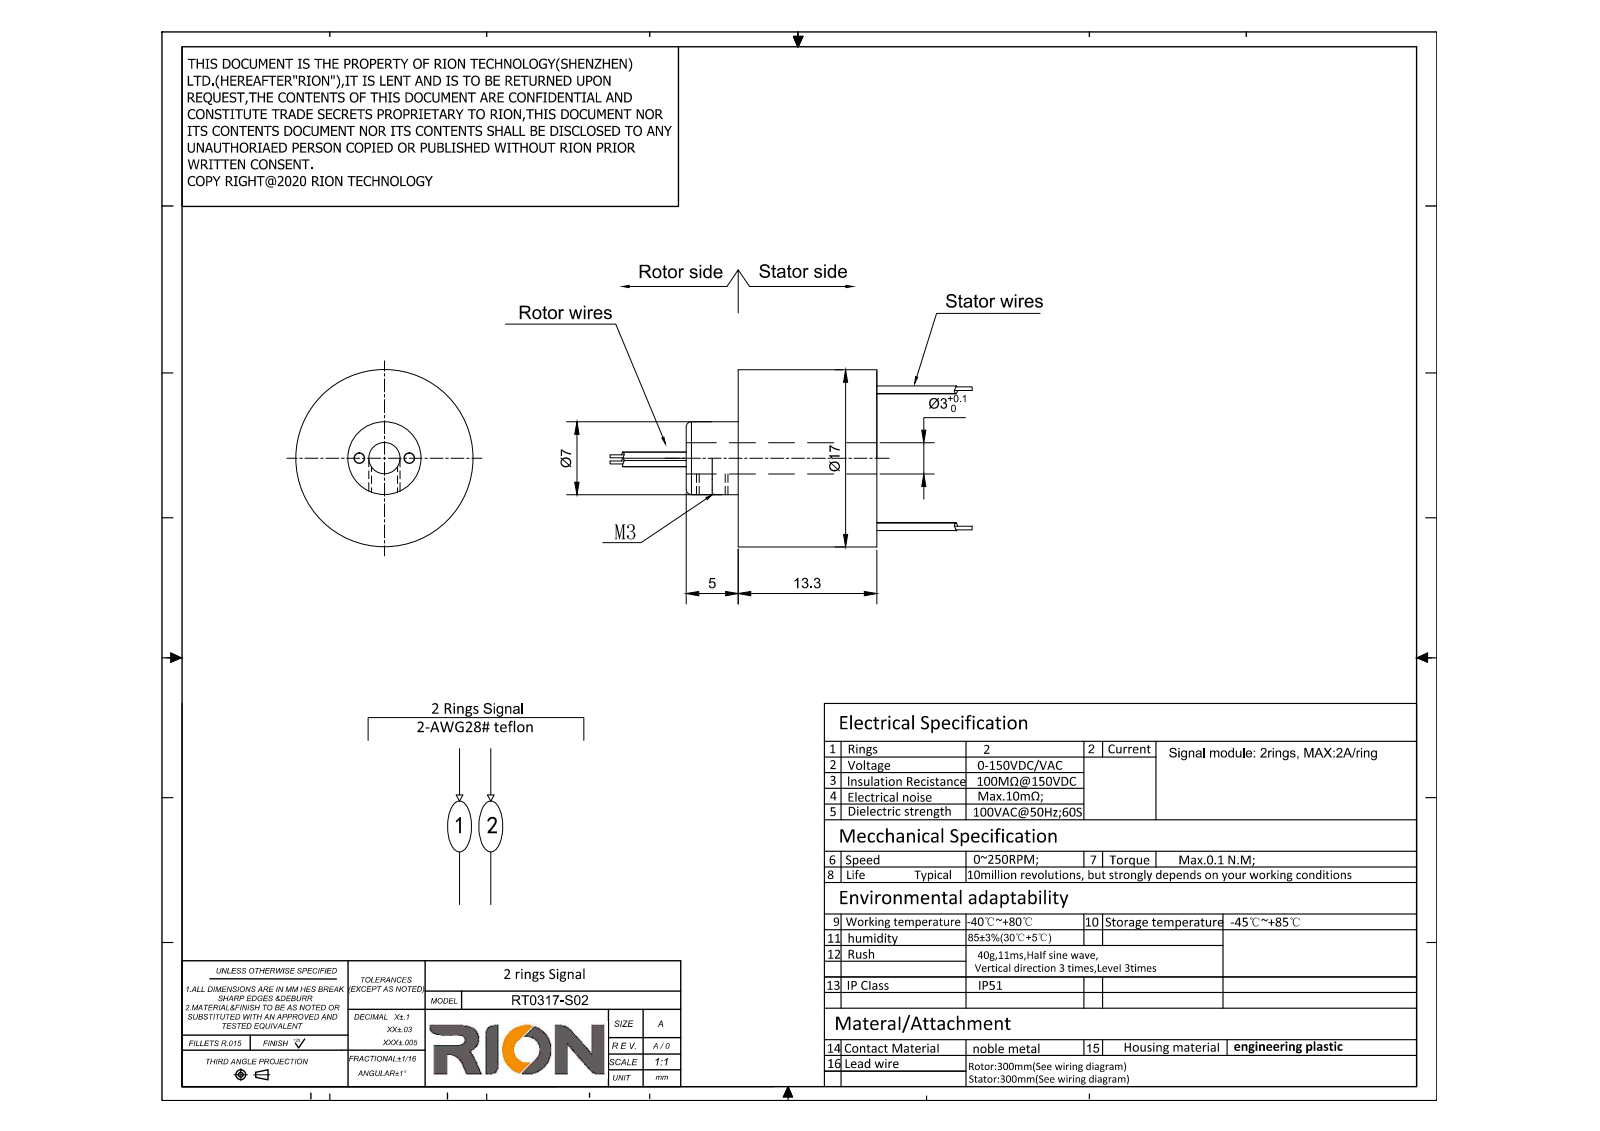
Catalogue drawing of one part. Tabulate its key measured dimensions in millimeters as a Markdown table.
| quantity | value |
| --- | --- |
| part name | RT0317-S02 |
| STEP written by | SolidWorks 2014 (AUTOMOTIVE_DESIGN) |
| units | millimeters |
| bodies | 1 solid, 48 faces (20 planar, 26 cylindrical, 2 other) |
| overall size | 27.8 × 17 × 17 |
| volume | 3 072 mm³ |
| surface area | 1 649 mm² |
| round holes (diameter × count) | 2.5 × 1, 3 × 1, 4.2 × 1, 7.1 × 1, 15 × 1 |
| round bosses / shafts (diameter × count) | 0.8 × 4, 17 × 1, 14.9 × 1, 7 × 1, 4 × 1 |
| main face-to-face distances | 13.3, 5, 18.3, 0.5, 1, 12.3, 17.8, 17.3, 12.8, 22.8 |
